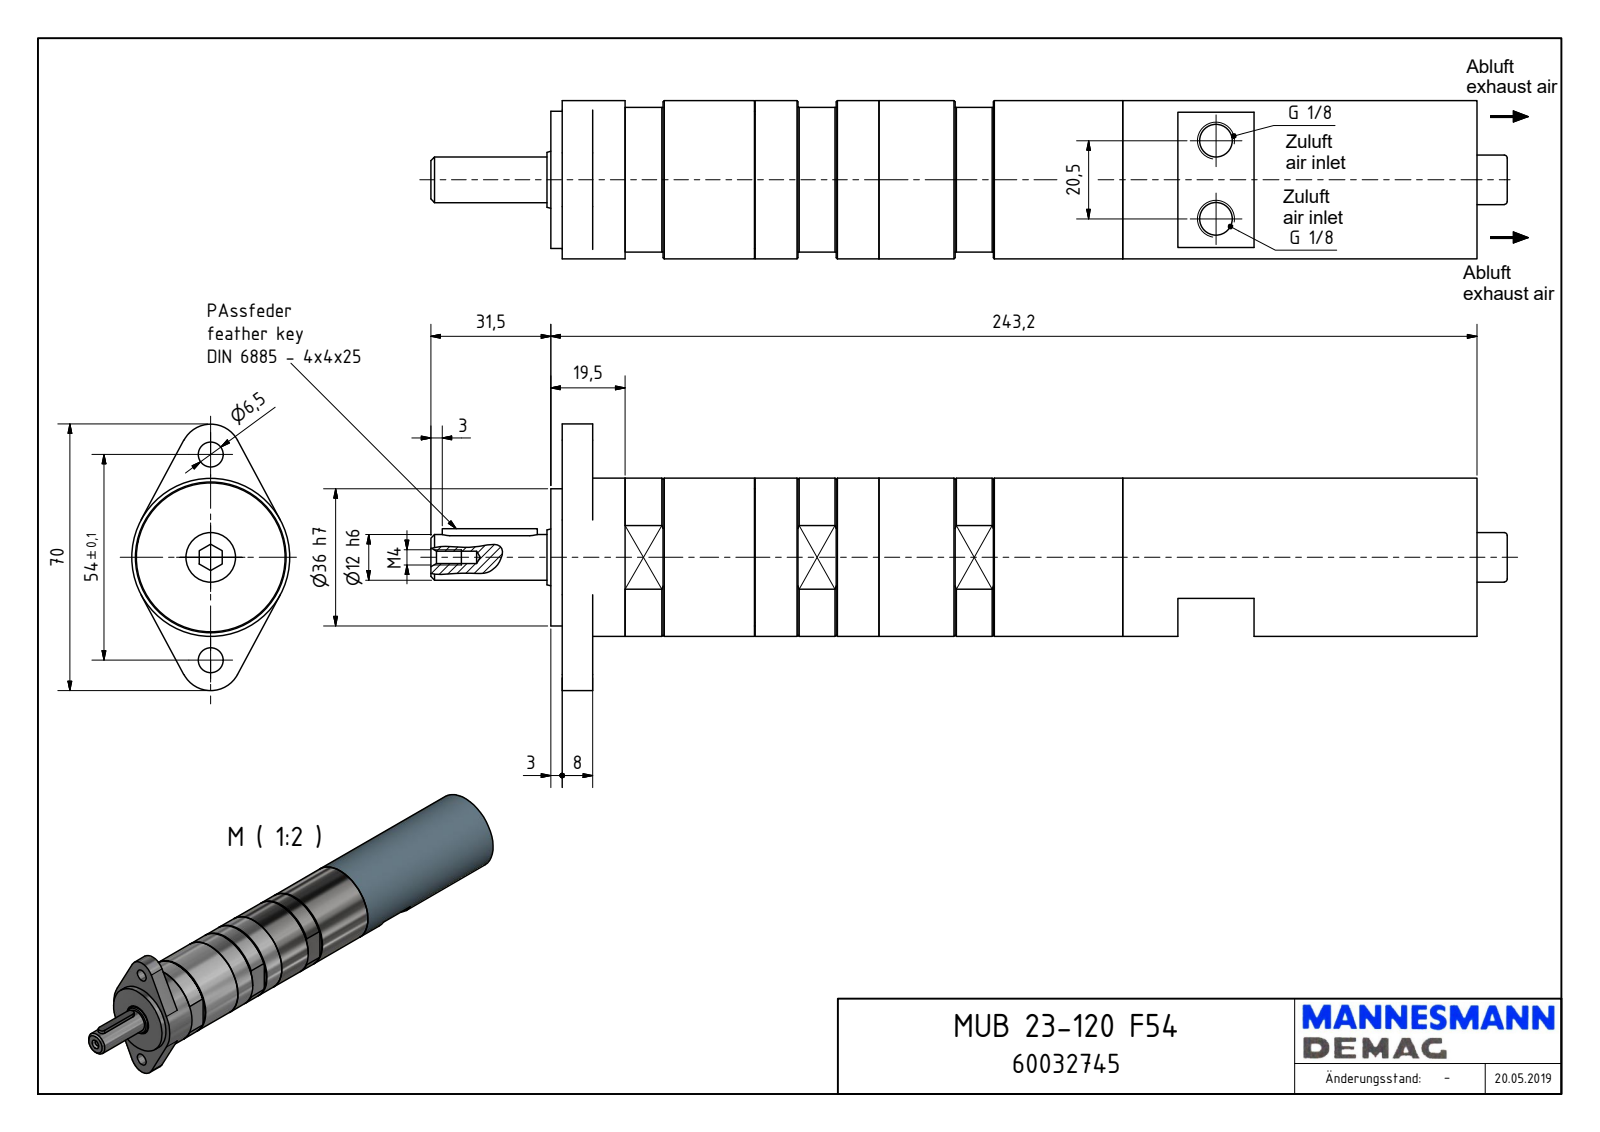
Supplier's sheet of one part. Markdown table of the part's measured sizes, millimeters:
| quantity | value |
| --- | --- |
| part name | MUB 23-120 F54_60032745 |
| STEP written by | Autodesk Inventor 2018 (AUTOMOTIVE_DESIGN) |
| units | millimeters |
| bodies | 1 solid, 151 faces (69 planar, 57 cylindrical, 25 other) |
| overall size | 282.7 × 70 × 41.5 |
| volume | 328 528 mm³ |
| surface area | 42 030 mm² |
| round holes (diameter × count) | 6.5 × 2, 8.57 × 2, 3.24 × 1, 8.5 × 1, 16 × 1, 39.5 × 1 |
| round bosses / shafts (diameter × count) | 41.5 × 1, 39 × 1, 36 × 1, 14.95 × 1, 13 × 1, 12 × 1, 8 × 1 |
| partial cylindrical surfaces (radius × count) | 2 × 4, 1 × 2, 1.6 × 2, 2.5 × 2, 8 × 2, 8.1 × 1, 12.74 × 1, 19.18 × 1 |
| main face-to-face distances | 240.2, 3, 243.2, 8, 11, 232.2, 38, 42.5, 41.48, 53.5 |
| hole center spacings | 27, 20.5, 54 |
